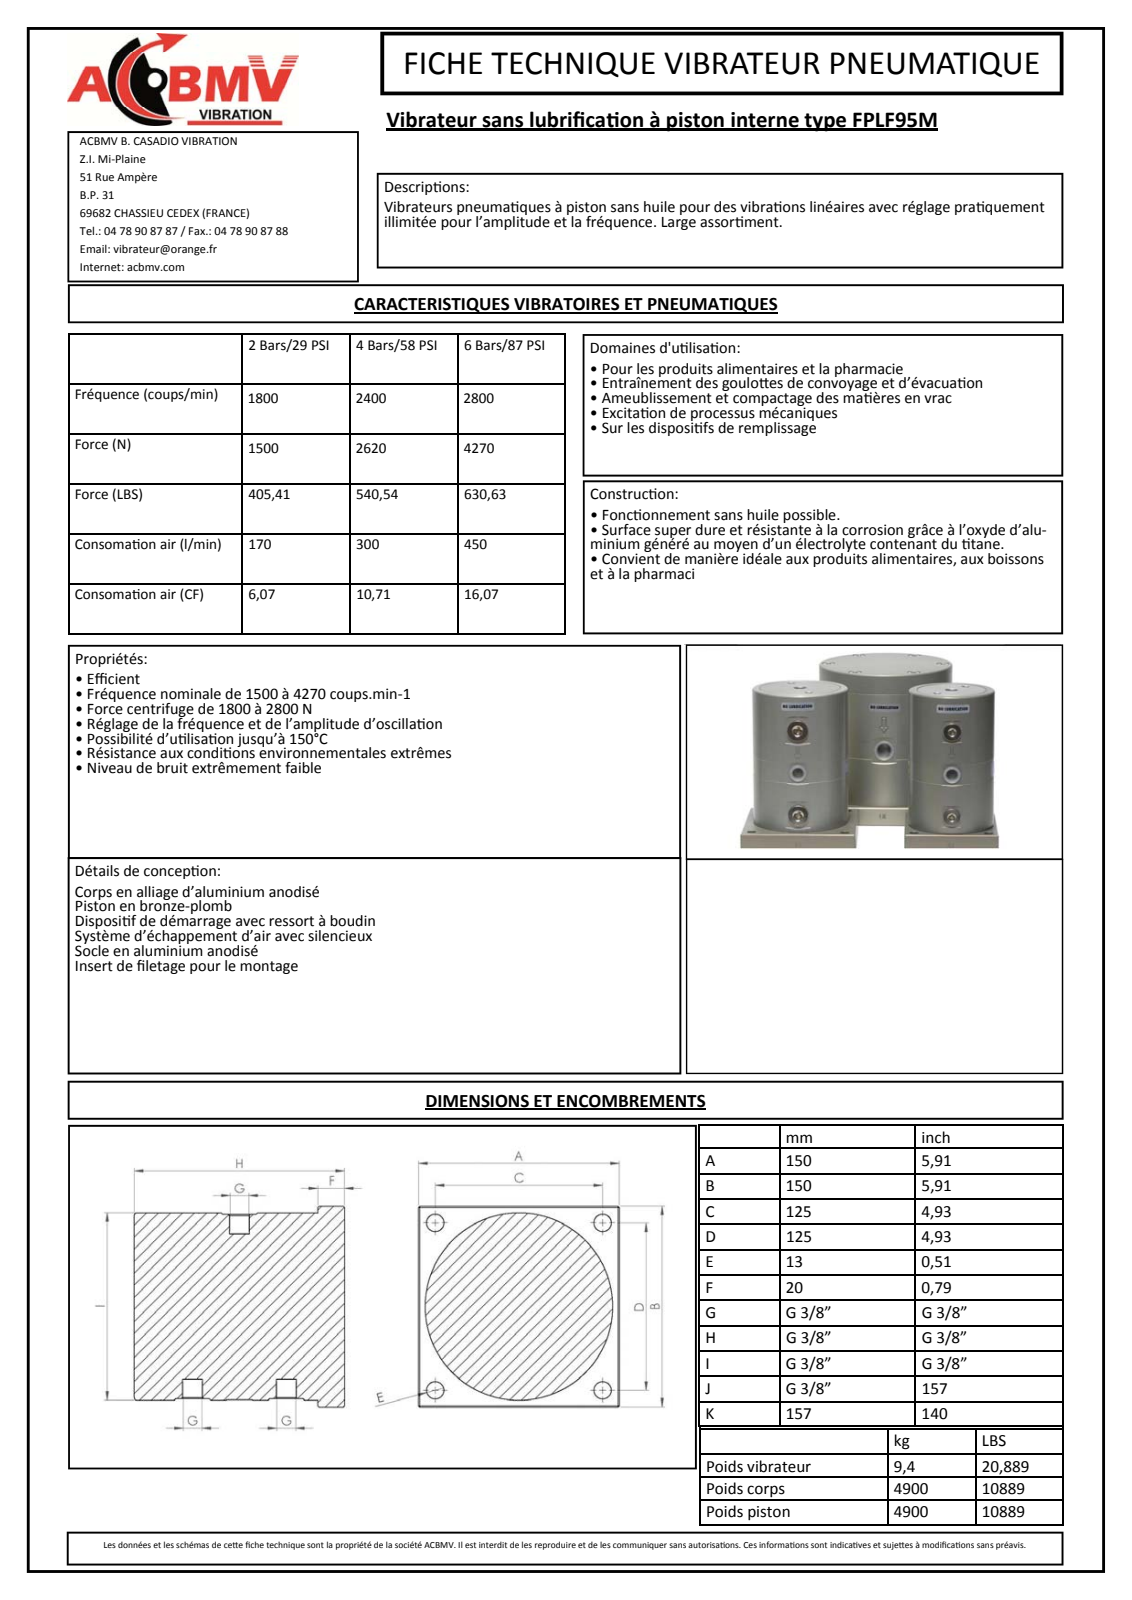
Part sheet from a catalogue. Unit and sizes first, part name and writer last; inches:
Units: inches
Overall size (bounding box): 6.181 × 5.906 × 5.906
Round holes (diameter × count): ⌀0.531 ×6, ⌀0.512 ×4, ⌀0.589 ×3
Round bosses / shafts (diameter × count): ⌀0.512 ×6, ⌀5.512 ×1, ⌀5.472 ×1
Partial cylindrical surfaces — rounded edges, fillets, slot ends (radius × count): R0.165 ×12, R0.008 ×7, R0.131 ×6, R0.157 ×6, R0.266 ×1, R2.126 ×1, R2.748 ×1
Main face-to-face distances: 6.181, 0.787, 5.394, 5.906, 0.244, 5.661, 0.016, 6.165, 4.676, 2.097
Hole centre spacings: 2.421, 4.194, 1.302, 2.461, 3.689, 4.726, 4.921, 5.467
Volume: 154.4 in³ · Surface area: 205.9 in²
Bodies: 1 solid, 466 faces (219 planar, 110 cylindrical, 137 other)
Part name (STEP PRODUCT): 9095-20-M
STEP written by: Autodesk Inventor 2011 (CONFIG_CONTROL_DESIGN)
